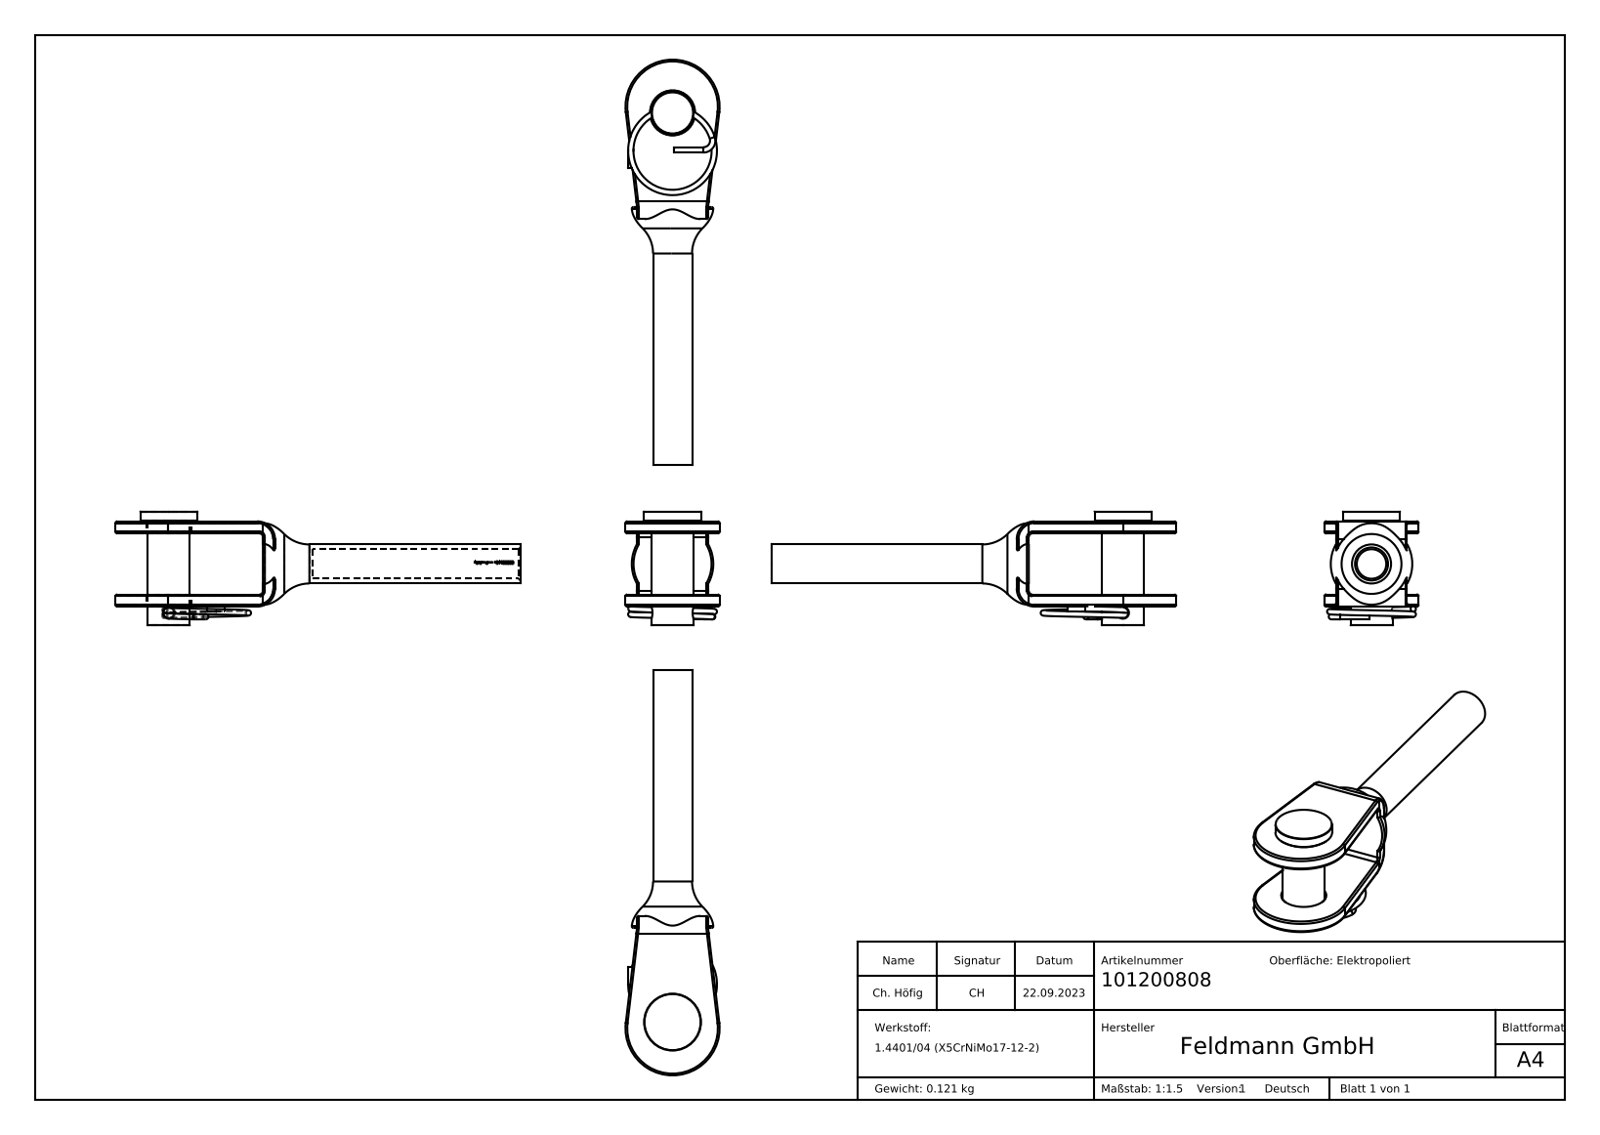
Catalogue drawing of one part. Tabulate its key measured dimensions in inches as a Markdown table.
| quantity | value |
| --- | --- |
| part name | 101200X0X Teil3_101200808 Teil3; 101200808; 101200X0X Teil1_101200808 Teil1; 101200X0X Teil2_101200808 Teil2 |
| STEP written by | SolidWorks 2018 (CONFIG_CONTROL_DESIGN) |
| units | inches |
| bodies | 3 solids, 322 faces (96 planar, 65 cylindrical, 161 other) |
| overall size | 4.488 × 1.26 × 1.043 |
| volume | 0.919 in³ |
| surface area | 17.48 in² |
| round holes (diameter × count) | 0.118 × 1, 0.327 × 1, 0.492 × 1 |
| round bosses / shafts (diameter × count) | 0.059 × 2, 0.63 × 1, 0.465 × 1, 0.433 × 1 |
| partial cylindrical surfaces (radius × count) | 0.02 × 12, 0.039 × 2, 0.197 × 2, 0.167 × 1, 0.522 × 1 |
| main face-to-face distances | 0.134, 0.811, 0.677, 0.945, 1.053, 0.919, 0.242, 0.108, 0.207, 0.341 |
